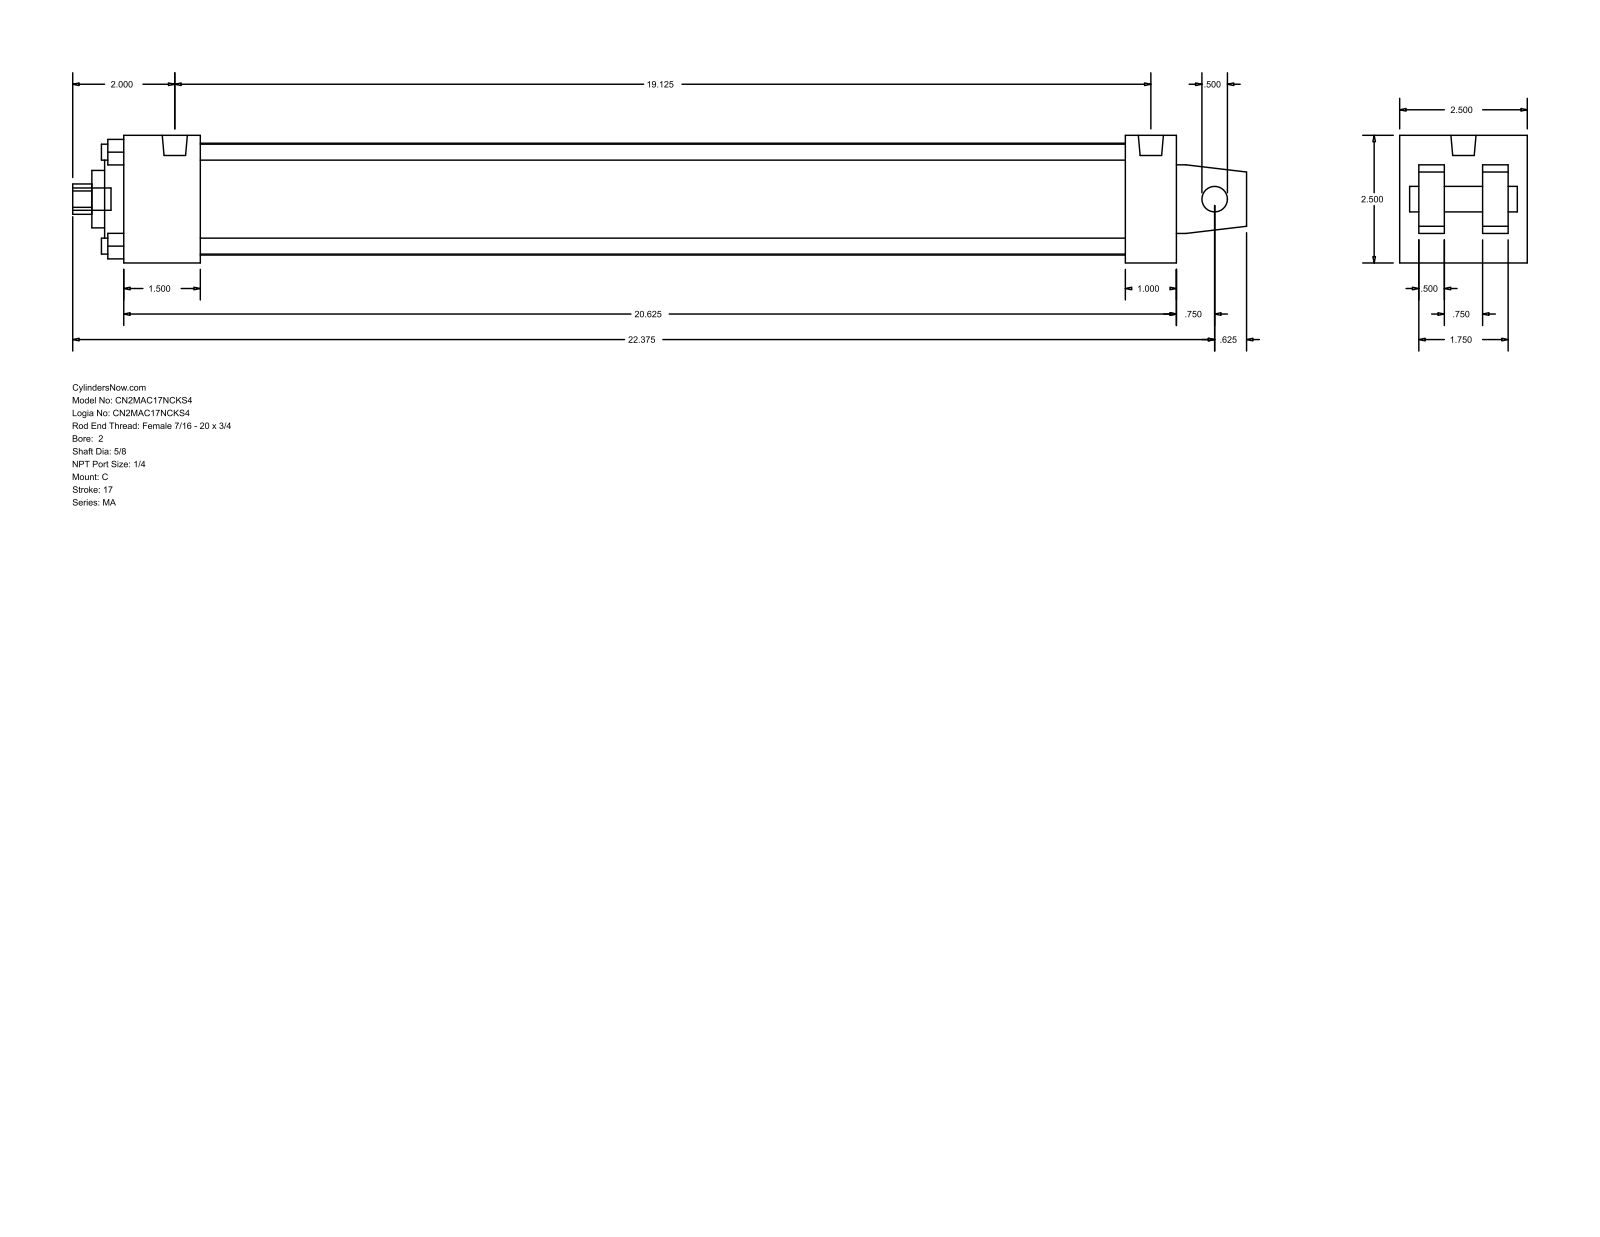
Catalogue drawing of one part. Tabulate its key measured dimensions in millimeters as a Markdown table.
| quantity | value |
| --- | --- |
| part name | MA_C__0200_0.625 |
| STEP written by | GSSL Pune (CONFIG_CONTROL_DESIGN) |
| units | millimeters |
| bodies | 0 solids, 105 faces (77 planar, 28 cylindrical, 0 other) |
| overall size | 584.2 × 63.5 × 63.5 |
| round holes (diameter × count) | 7.94 × 4, 12.7 × 1, 15.88 × 1, 28.57 × 1, 50.8 × 1, 55.63 × 1 |
| round bosses / shafts (diameter × count) | 7.94 × 4, 12.49 × 2, 11.11 × 1 |
| partial cylindrical surfaces (radius × count) | 7.54 × 1 |
| main face-to-face distances | 63.5, 9.52, 12.7, 22.22, 41.28, 53.98, 31.76, 38.1, 523.87, 485.77 |
| hole center spacings | 33.05, 46.74, 66.1 |
